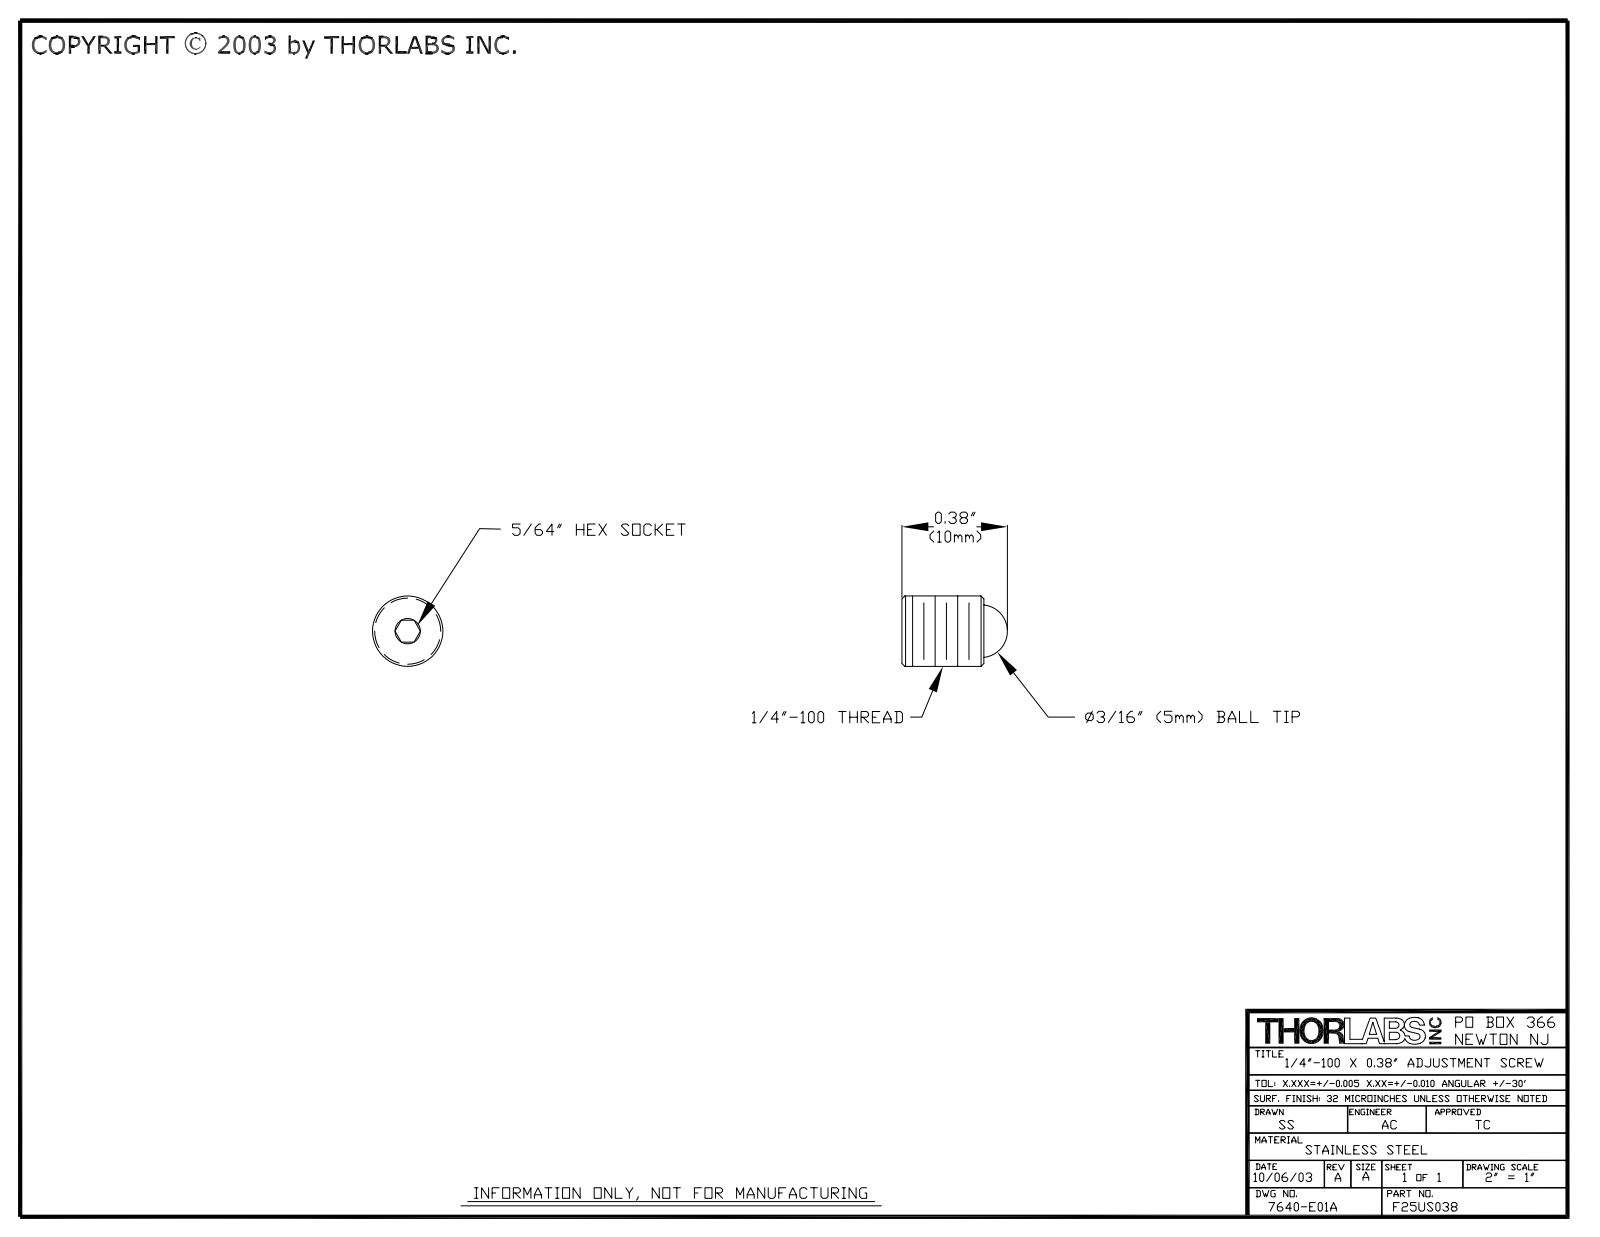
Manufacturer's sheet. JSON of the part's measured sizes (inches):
{"part_name": "7640-E0W", "step_written_by": "SolidWorks 2007 (AUTOMOTIVE_DESIGN)", "units": "inches", "bodies": {"solids": 0, "faces": 20, "planar": 8, "cylindrical": 4, "other": 8}, "overall_size": [0.385, 0.25, 0.25], "round_holes": [[0.187, 1]], "round_bosses_or_shafts": [[0.25, 1]], "face_to_face_distances": [0.078, 0.301]}
